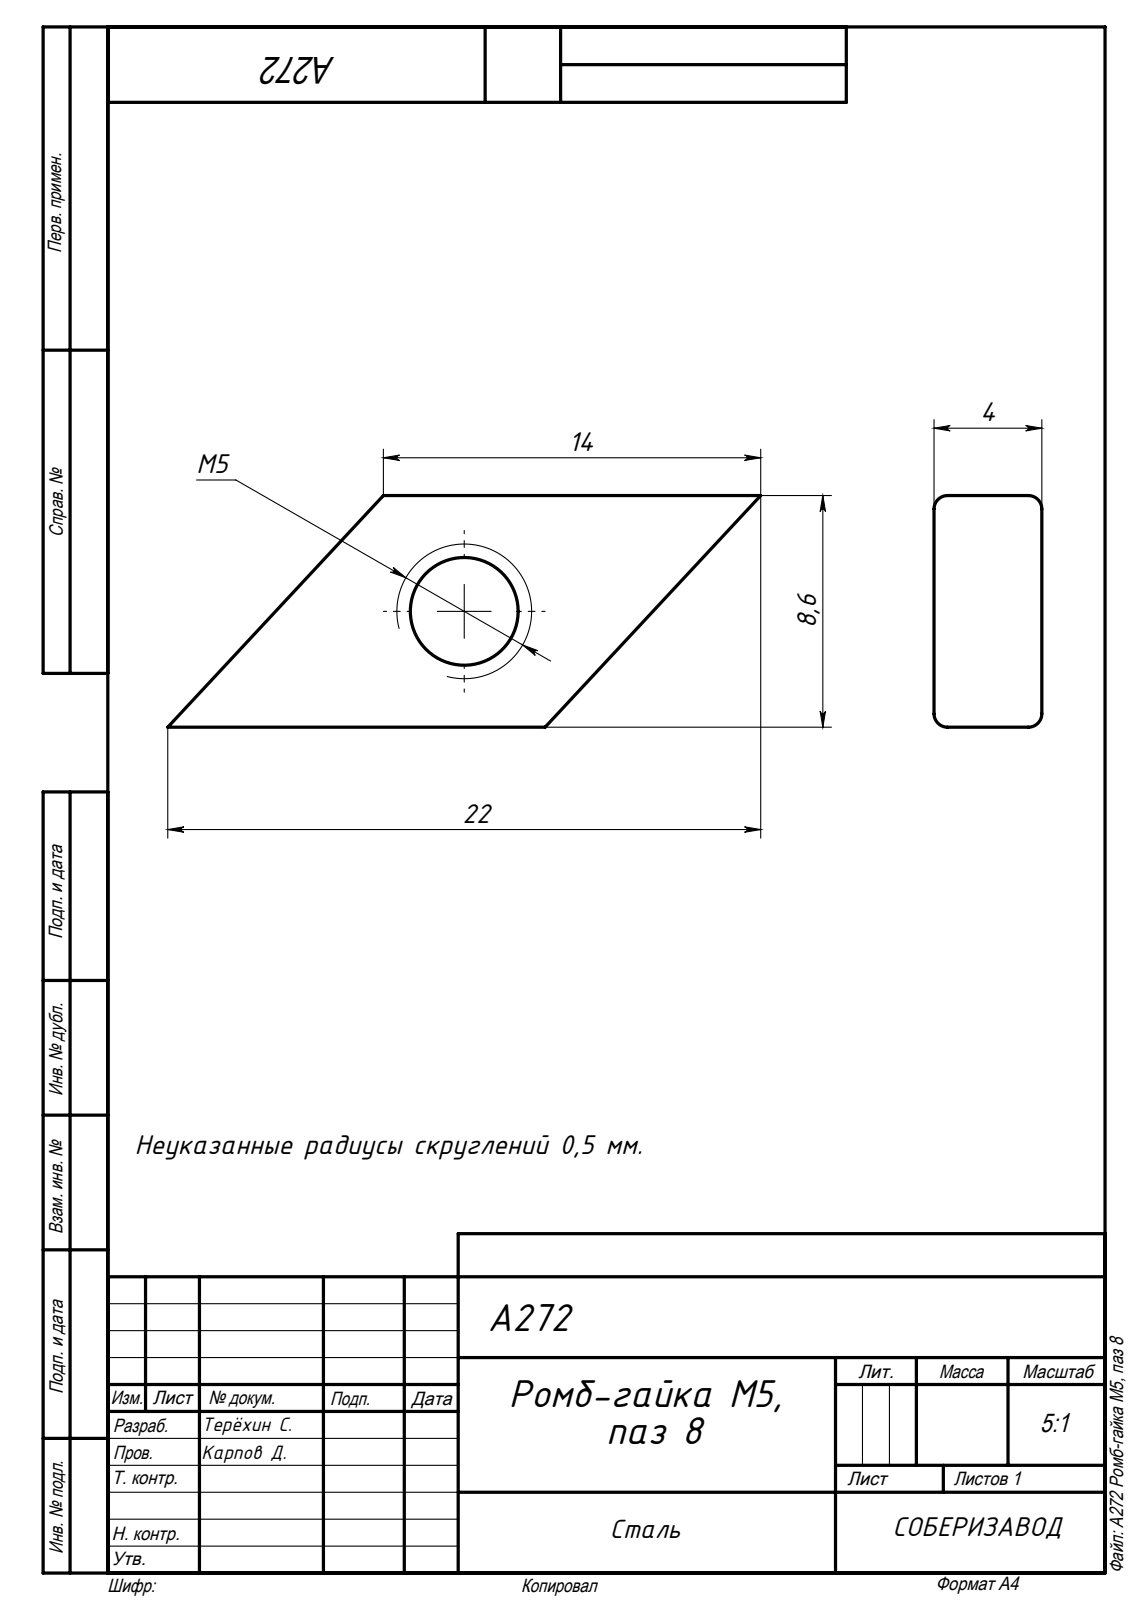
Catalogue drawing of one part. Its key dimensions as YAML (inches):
part_name: "A272 Ромб-гайка М5, паз 8"
step_written_by: "SolidWorks 2020 (AUTOMOTIVE_DESIGN)"
units: inches
bodies: {solids: 1, faces: 16, planar: 6, cylindrical: 10, other: 0}
overall_size: [0.866, 0.339, 0.157]
volume: 0.026
surface_area: 0.696
round_holes:
  - {diameter: 0.157, count: 1}
partial_cylinders:
  - {radius: 0.02, count: 8}
face_to_face_distances: [0.157, 0.339, 0.403]
